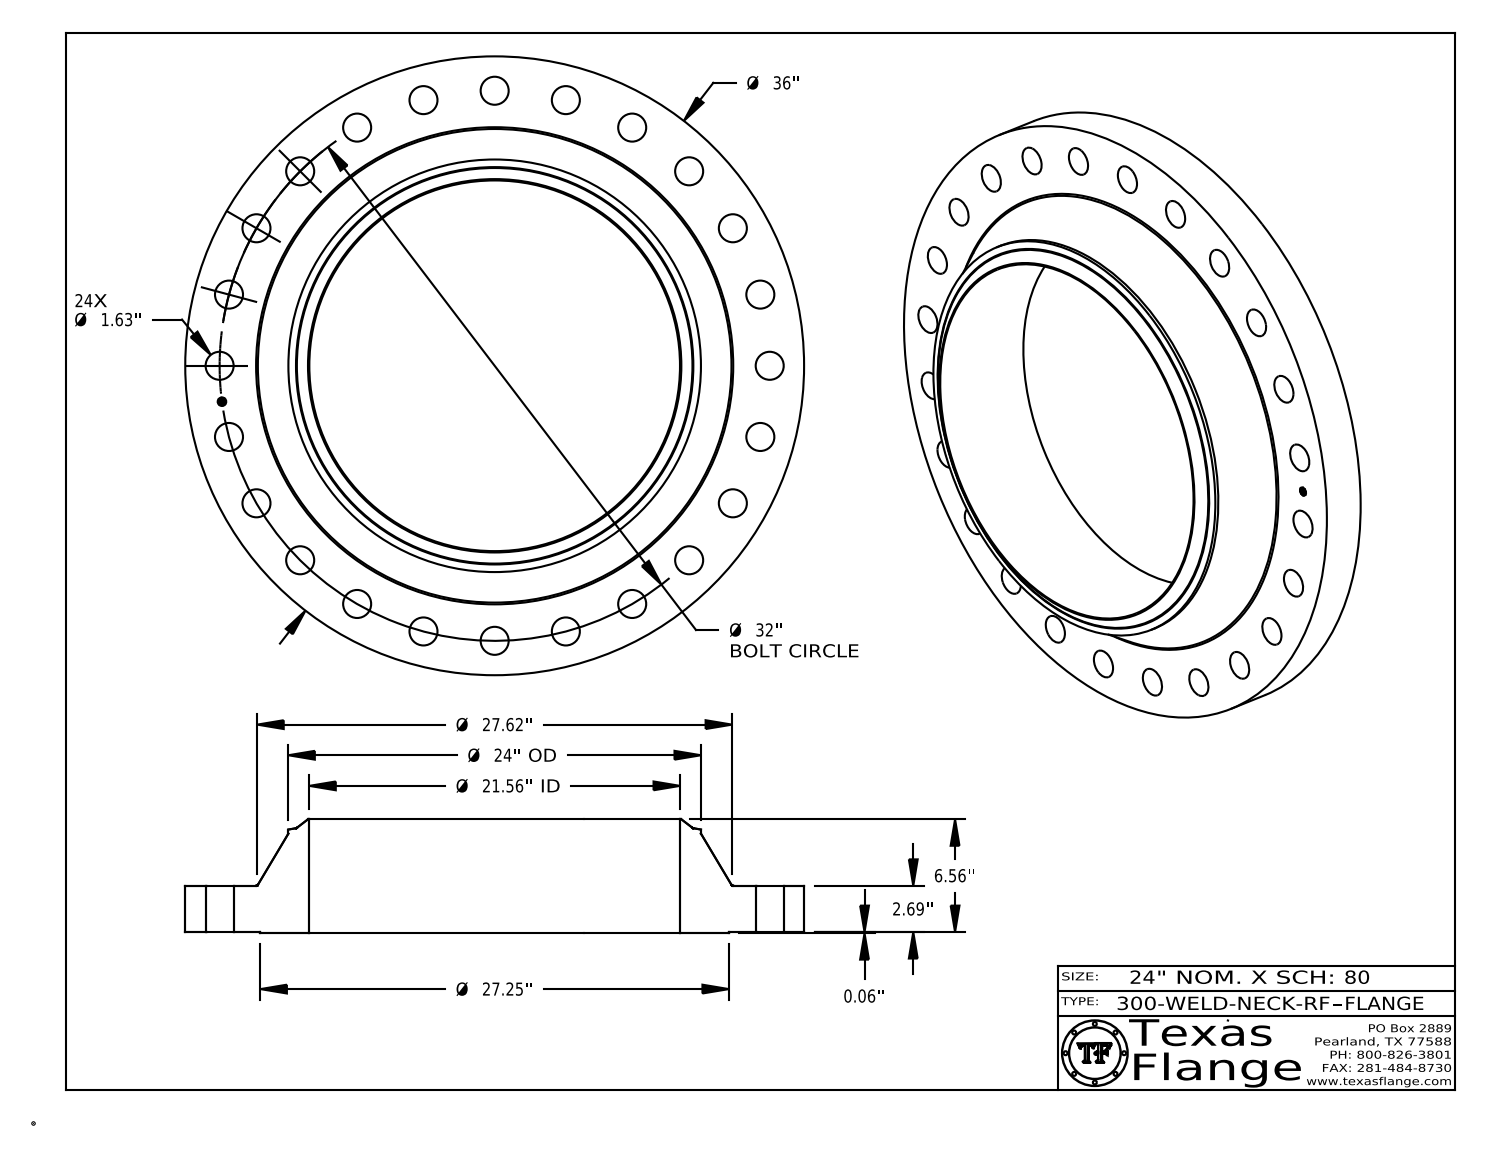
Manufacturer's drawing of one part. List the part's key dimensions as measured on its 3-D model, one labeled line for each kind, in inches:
Part name (STEP PRODUCT): 300-WELD-NECK-RF
STEP written by: CATIA V5 STEP AP214 (AUTOMOTIVE_DESIGN)
Units: inches
Bodies: 1 solid, 455 faces (369 planar, 76 cylindrical, 10 other)
Overall size (bounding box): 36 × 36 × 6.623
Volume: 2 159 in³ · Surface area: 2 464 in²
Round holes (diameter × count): ⌀1.63 ×24, ⌀0.495 ×1, ⌀21.562 ×1
Round bosses / shafts (diameter × count): ⌀0.03 ×8, ⌀36 ×1, ⌀27.25 ×1, ⌀24 ×1, ⌀0.39 ×1
Main face-to-face distances: 2.69, 0.063, 2.753, 6.622, 6.56, 3.87, 2.738, 2.675, 0.015, 3.885
Hole centre spacings: 16, 30.909, 4.177, 8.282, 12.246, 19.48, 22.627, 25.387
